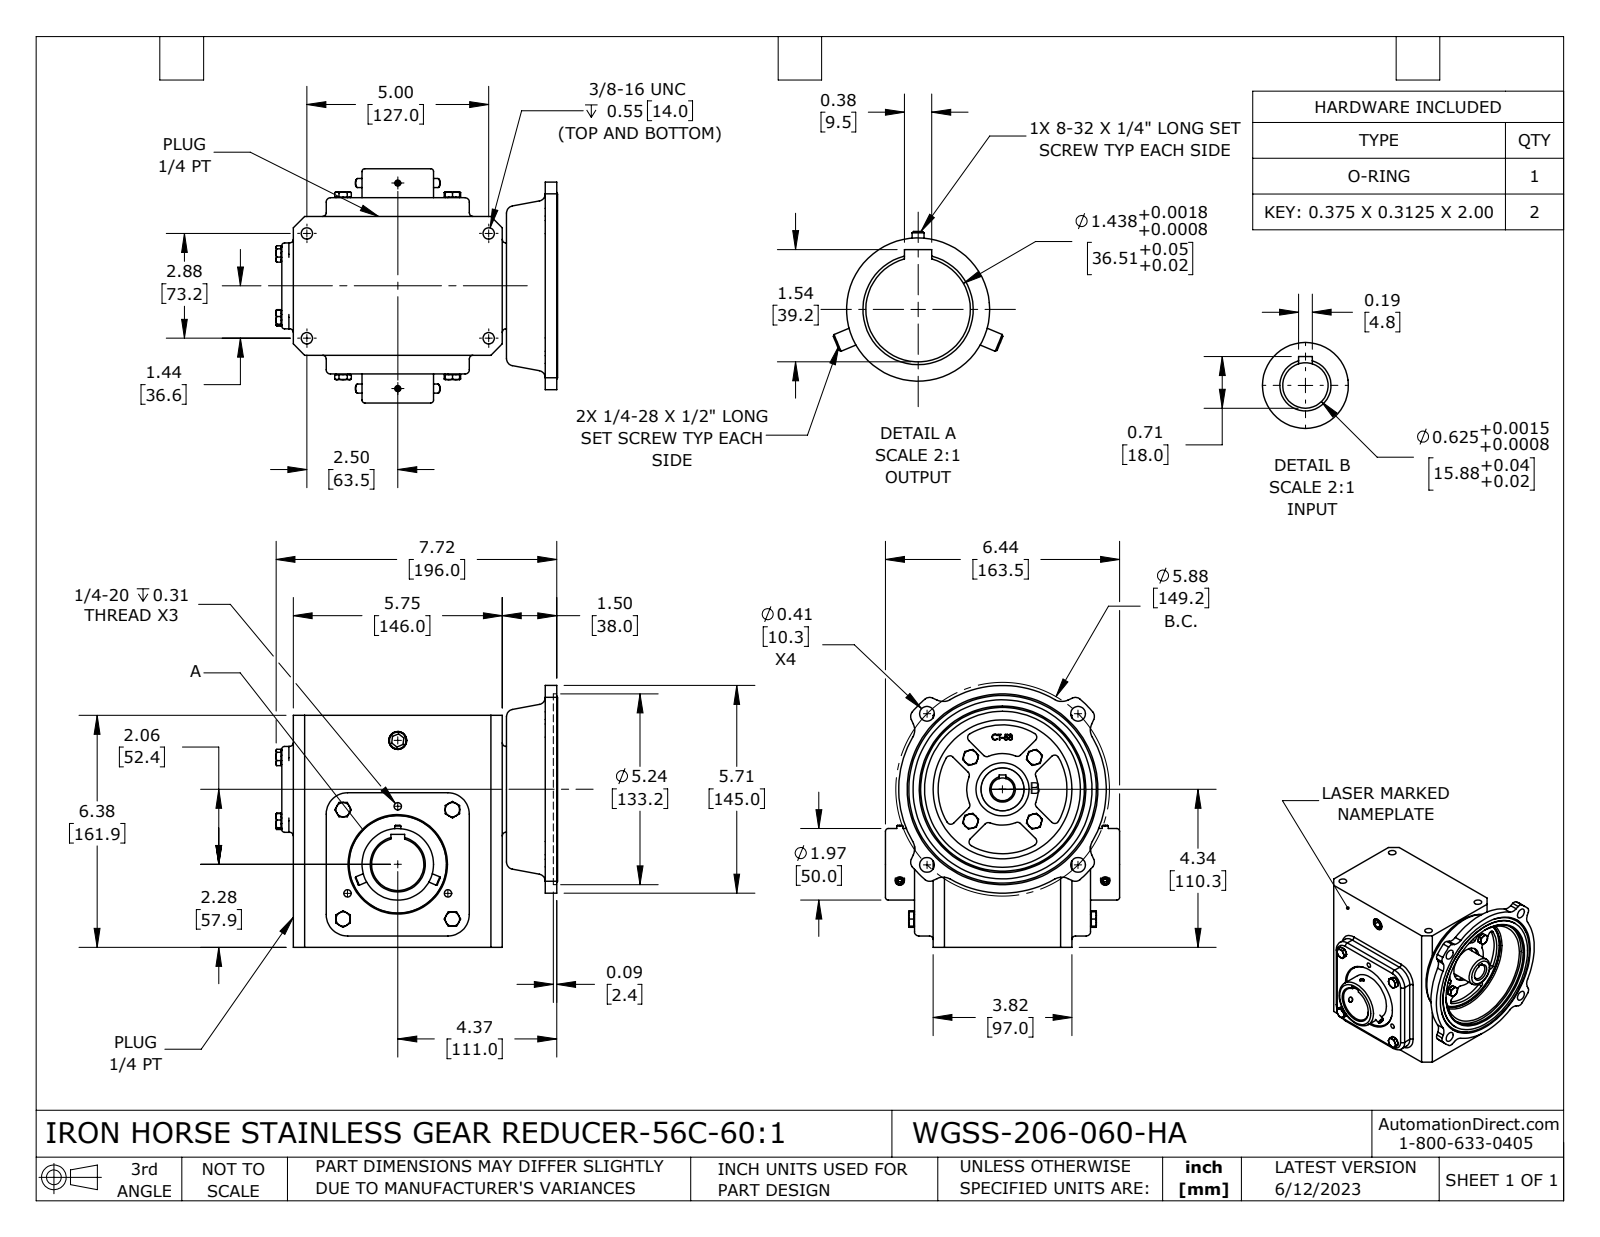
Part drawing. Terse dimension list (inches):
name: WGSS-206-060-HA
written by: SolidWorks 2021 (CONFIG_CONTROL_DESIGN)
unit: in
bodies: 7 solids, 895 faces (396 planar, 235 cylindrical, 264 other)
size: 7.74 × 7.197 × 6.437
volume: 159.7 in³; area: 323.7 in²
holes: 4× ⌀0.213, 4× ⌀0.313, 4× ⌀0.406, 3× ⌀0.201, 2× ⌀0.136, 1× ⌀0.625, 1× ⌀0.866, 1× ⌀1.437, 1× ⌀1.441, 1× ⌀1.457, 1× ⌀1.575, 1× ⌀3.819
bosses: 8× ⌀0.394, 4× ⌀0.25, 2× ⌀0.164, 1× ⌀4.921, 1× ⌀2.677, 1× ⌀1.969, 1× ⌀1.181
rounds: 24× R0.118, 16× R0.098, 12× R0.394, 8× R0.197, 4× R0.079, 4× R0.315, 4× R0.591, 1× R0.984
face distances: 6.375, 3.819, 0.512, 4.331, 5.748, 0.118, 0.315, 7.244, 4.843, 0.157
hole spacings: 2.858, 2.937, 4.154, 4.944, 1.594, 5.65, 2.762, 2.88
